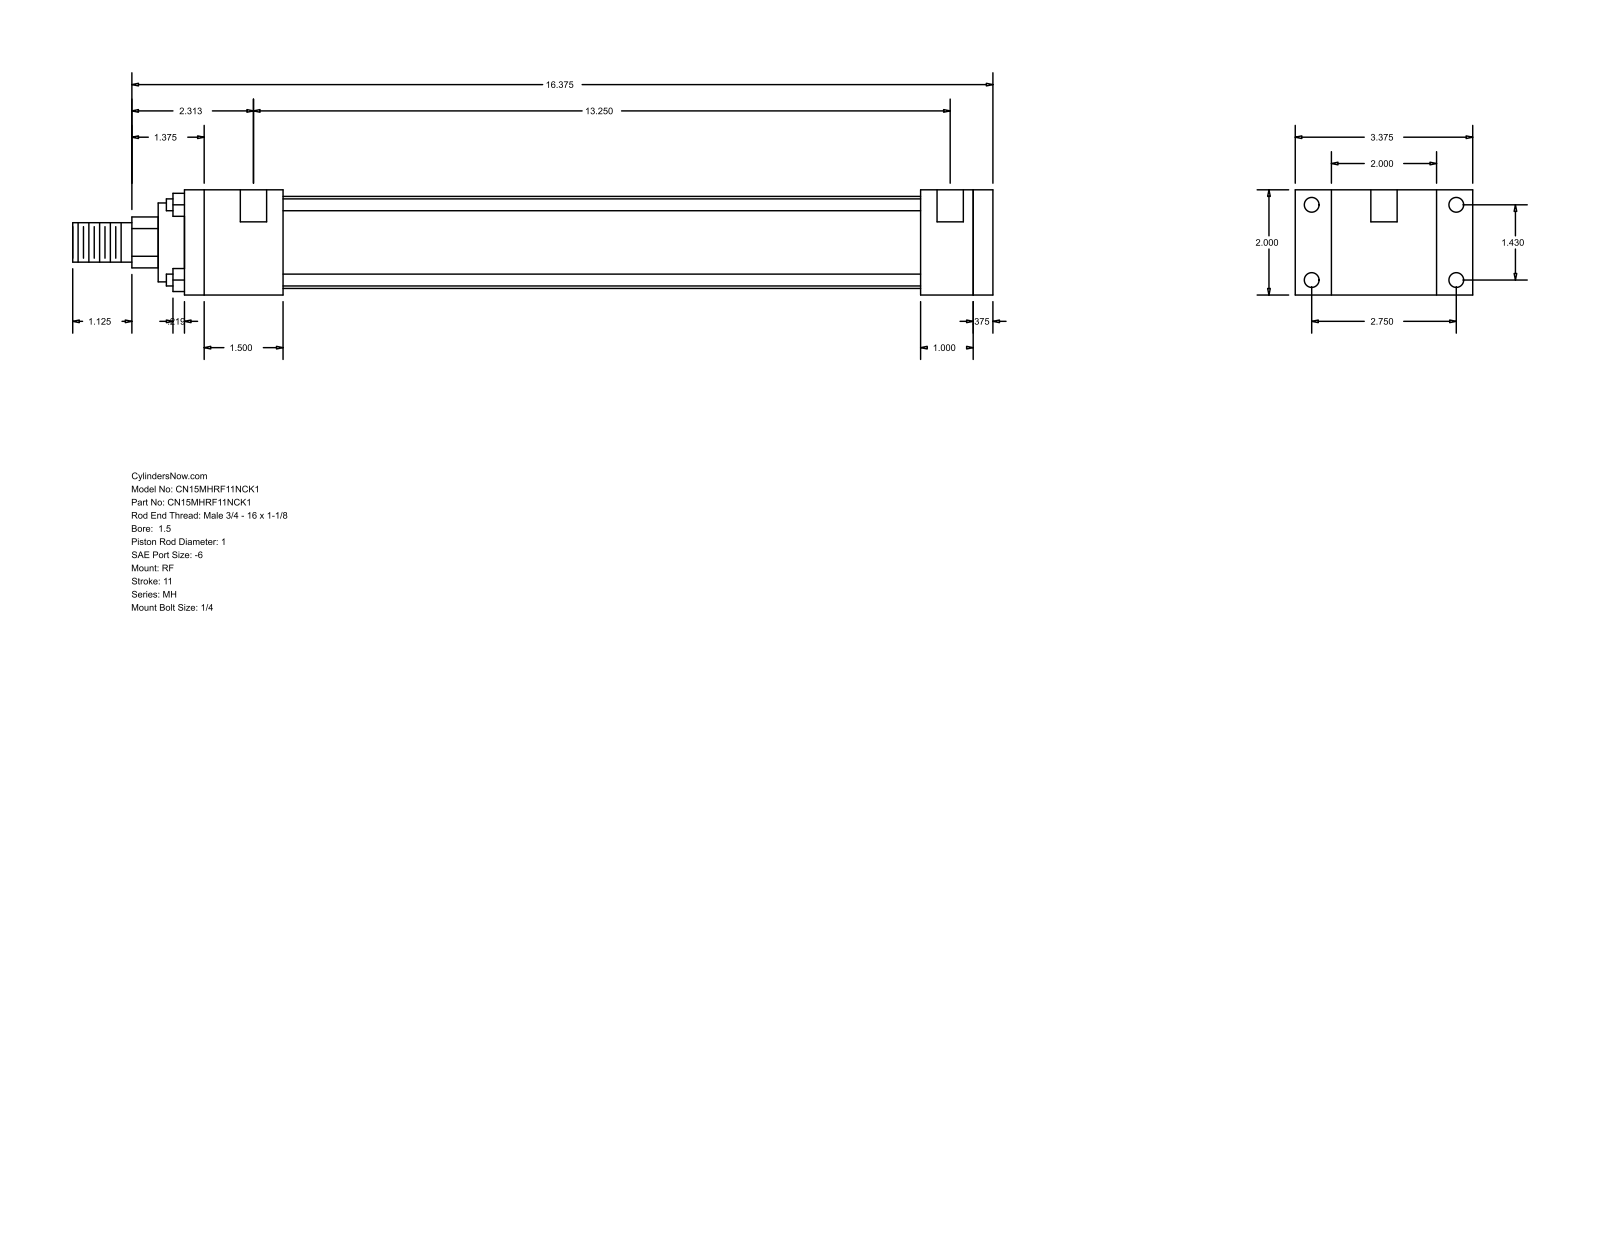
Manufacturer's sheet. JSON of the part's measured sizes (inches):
{"part_name": "MH_RF__0150_1", "step_written_by": "GSSL Pune (CONFIG_CONTROL_DESIGN)", "units": "inches", "bodies": {"solids": 0, "faces": 92, "planar": 64, "cylindrical": 28, "other": 0}, "overall_size": [17.5, 3.375, 2], "round_holes": [[0.219, 4], [0.281, 4], [0.5, 2]], "round_bosses_or_shafts": [[0.225, 4], [1.75, 1], [1.5, 1], [1, 1], [0.75, 1]], "partial_cylinders_radius": [[0.484, 1]], "face_to_face_distances": [2, 0.375, 15, 1, 15.375, 0.687, 2.687, 14, 1.375, 1.875], "hole_center_spacings": [1.43, 2.75, 3.099, 13.375, 0.125, 13.25]}
